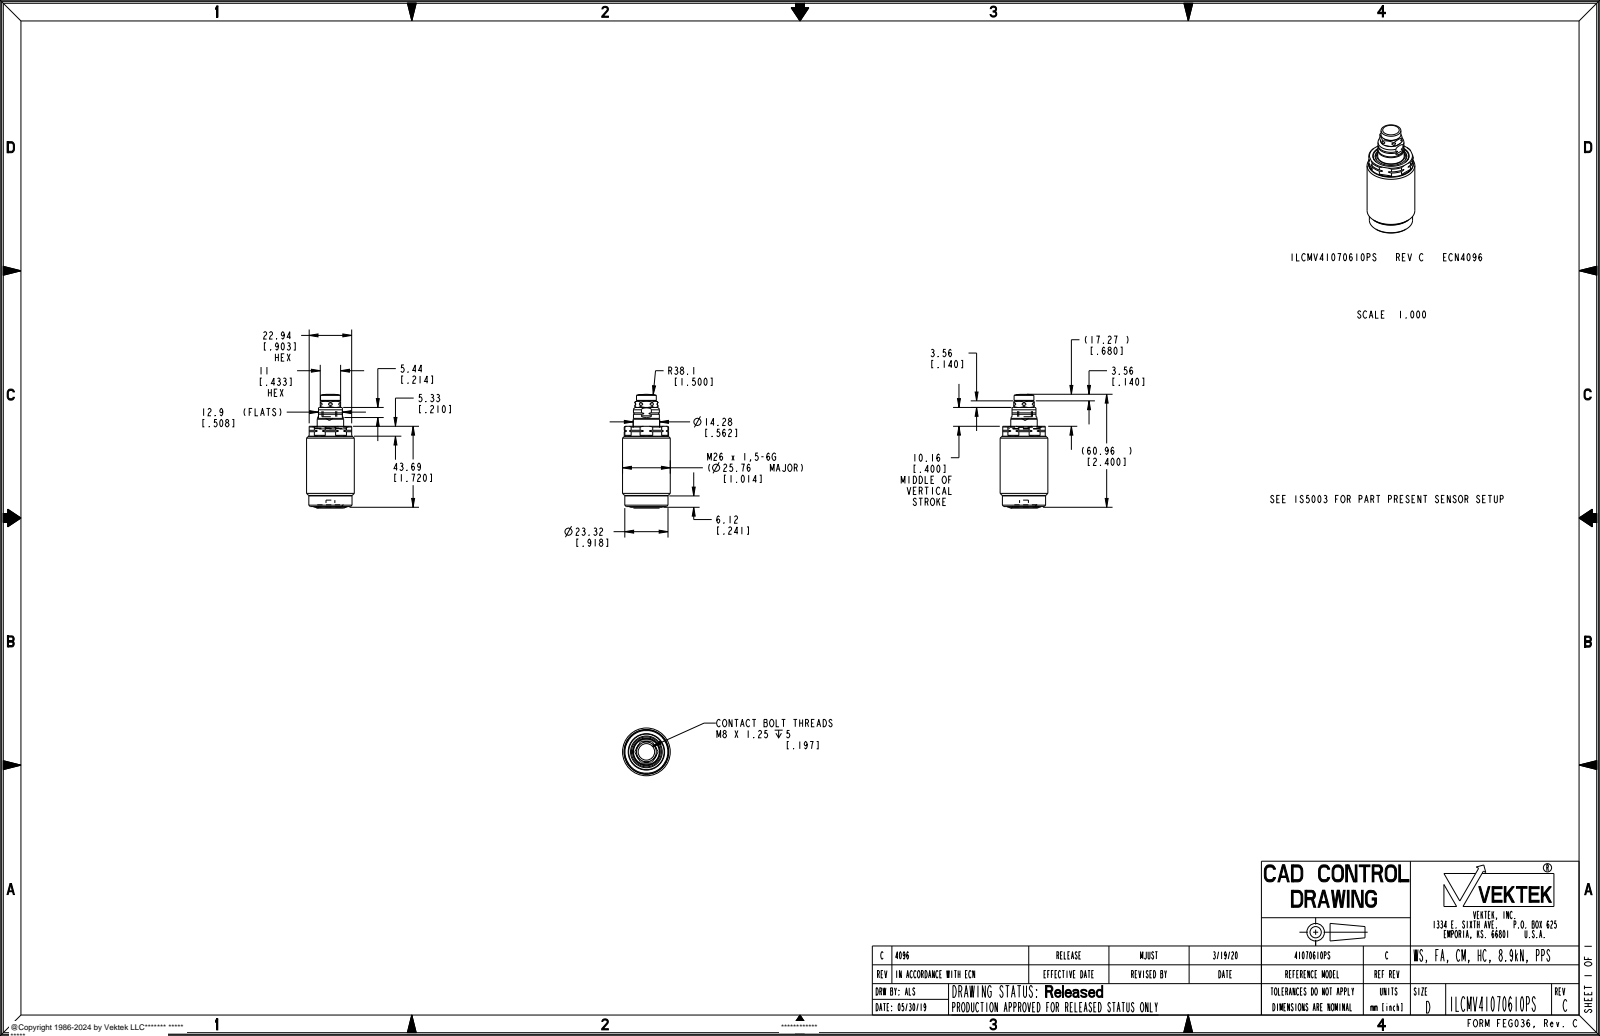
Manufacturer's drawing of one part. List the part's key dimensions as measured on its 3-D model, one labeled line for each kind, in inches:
Part name (STEP PRODUCT): ILCMV41070610PS
STEP written by: PRO/ENGINEER BY PARAMETRIC TECHNOLOGY CORPORATION, 2017170 (AUTOMOTIVE_DESIGN)
Units: inches
Bodies: 1 solid, 139 faces (29 planar, 52 cylindrical, 58 other)
Overall size (bounding box): 2.418 × 1.014 × 1.014
Volume: 1.431 in³ · Surface area: 8.248 in²
Round holes (diameter × count): ⌀0.188 ×1, ⌀0.625 ×1, ⌀0.674 ×1
Round bosses / shafts (diameter × count): ⌀1.014 ×1, ⌀0.942 ×1, ⌀0.918 ×1, ⌀0.754 ×1, ⌀0.562 ×1, ⌀0.55 ×1, ⌀0.42 ×1
Partial cylindrical surfaces — rounded edges, fillets, slot ends (radius × count): R0.018 ×6, R0.036 ×2, R0.245 ×1
Main face-to-face distances: 1.668, 0.037, 1.705, 0.235, 0.668, 0.903, 1.694, 1.657, 0.433, 0.015
